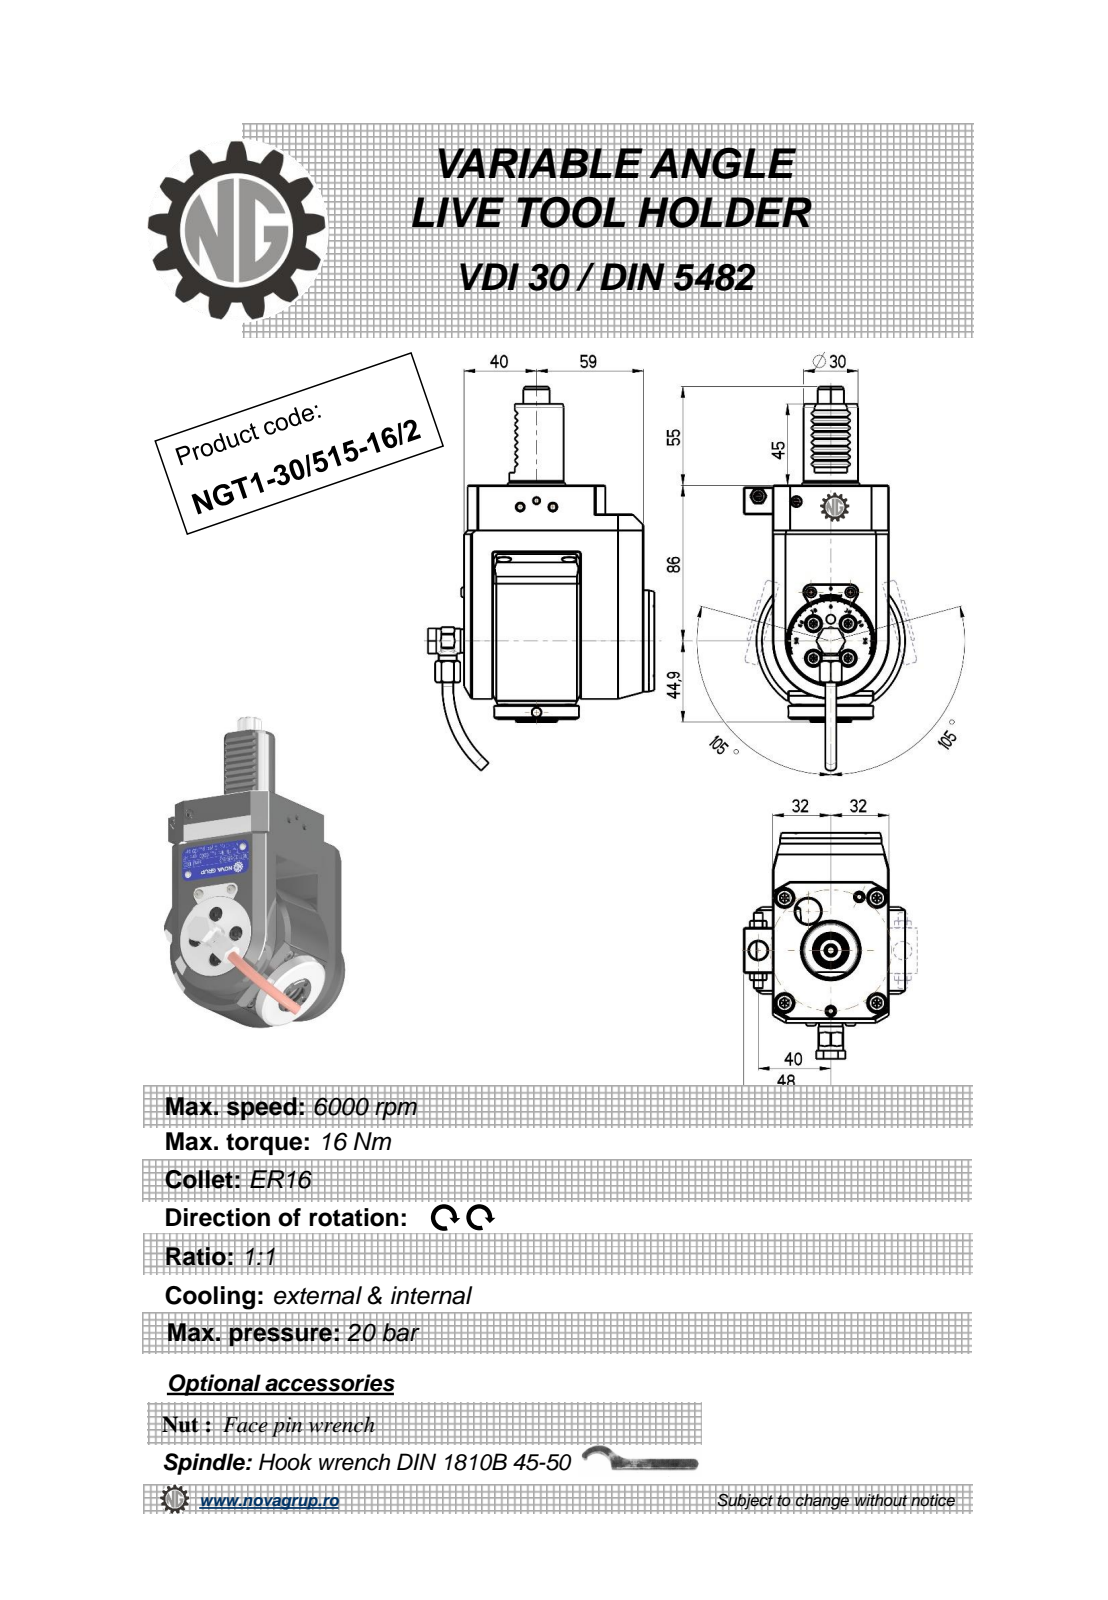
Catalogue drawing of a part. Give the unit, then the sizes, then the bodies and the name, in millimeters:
Units: millimetres
Overall size (bounding box): 212.67 × 124.9 × 89
Round holes (diameter × count): ⌀3.2 ×4, ⌀4 ×3, ⌀4.2 ×2, ⌀5 ×2, ⌀10 ×2, ⌀3 ×1, ⌀5.3 ×1, ⌀6.2 ×1, ⌀9 ×1, ⌀9.5 ×1, ⌀11 ×1, ⌀12.5 ×1
Round bosses / shafts (diameter × count): ⌀6 ×2, ⌀5.7 ×2, ⌀56 ×1, ⌀47 ×1, ⌀35 ×1, ⌀30 ×1, ⌀23 ×1, ⌀13.6 ×1
Partial cylindrical surfaces — rounded edges, fillets, slot ends (radius × count): R2.91 ×16, R0.26 ×12, R0.3 ×8, R0.16 ×6, R0.5 ×4, R1 ×2, R5.75 ×1, R7.25 ×1
Main face-to-face distances: 64, 16, 37, 99, 6, 105, 21, 14, 62, 35
Hole centre spacings: 9.25, 13.08, 18.5, 41.06, 49.87, 50.26, 0.4, 30.75
Volume: 769 716 mm³ · Surface area: 70 582 mm²
Bodies: 1 solid, 528 faces (199 planar, 166 cylindrical, 163 other)
Part name (STEP PRODUCT): NGT1_30_515_16_2
STEP written by: PRO/ENGINEER BY PARAMETRIC TECHNOLOGY CORPORATION, 2010280 (CONFIG_CONTROL_DESIGN)
